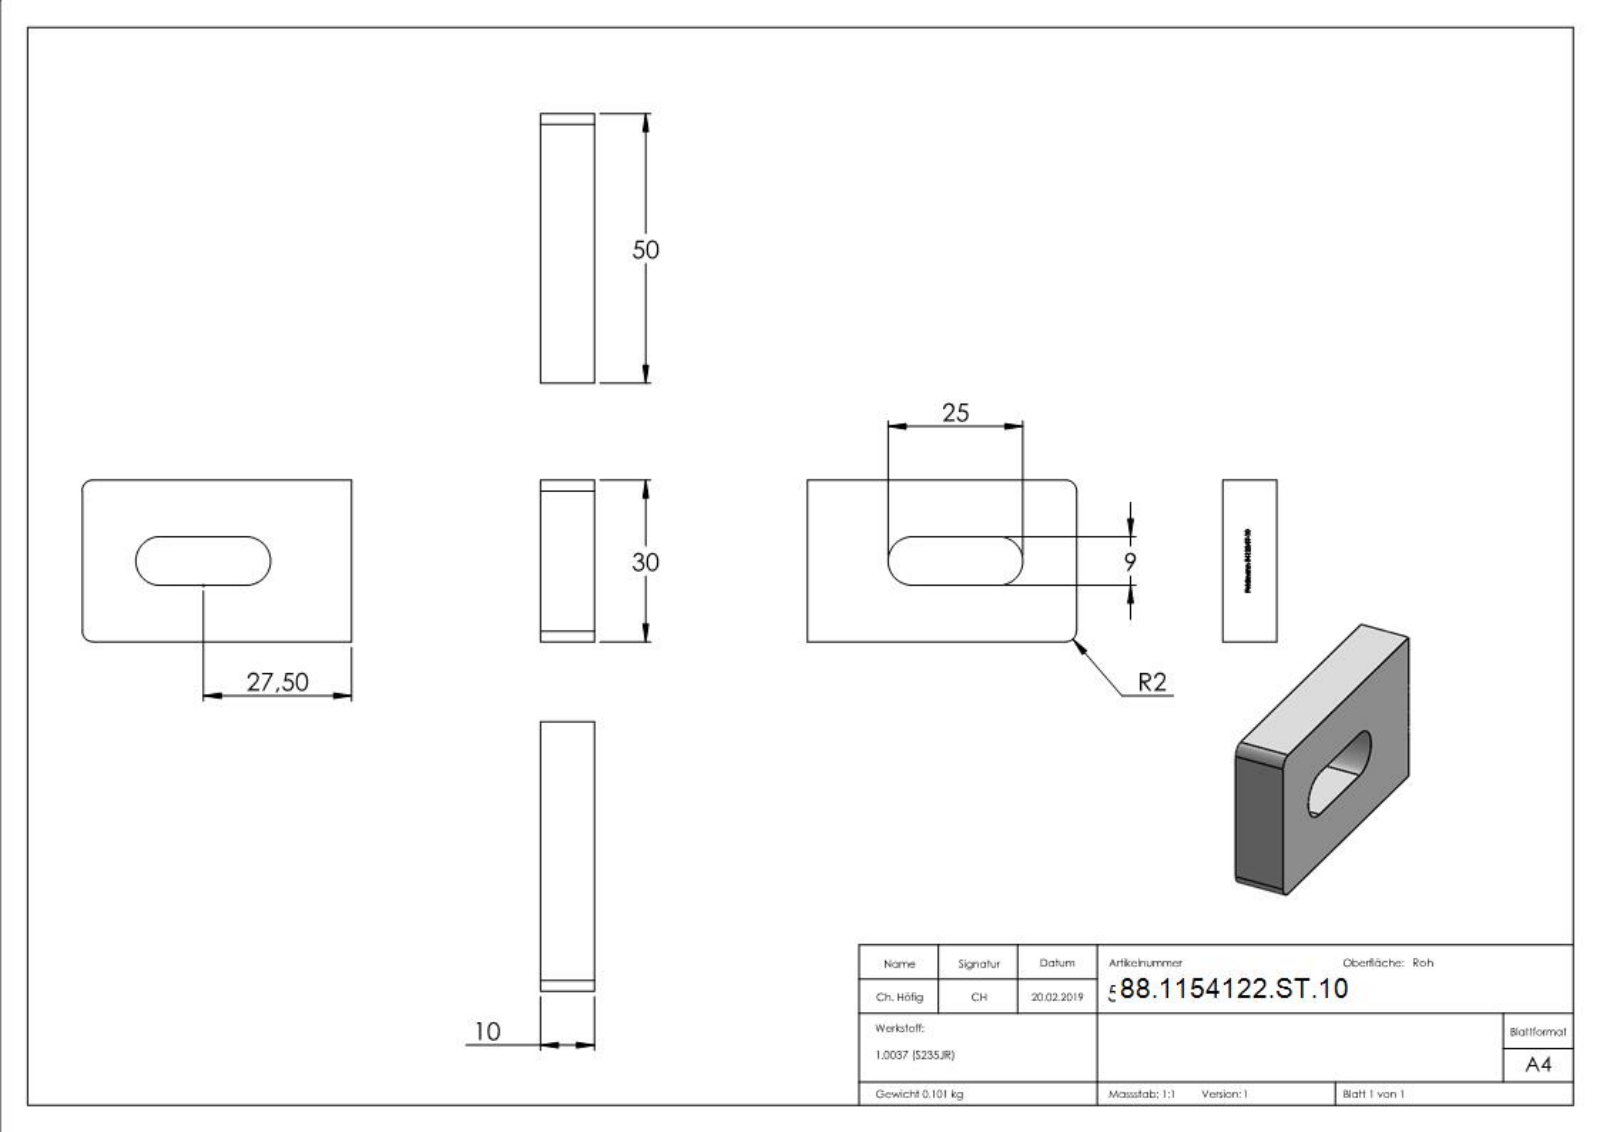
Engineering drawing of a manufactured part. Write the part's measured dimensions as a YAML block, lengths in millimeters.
part_name: "54122-ST-10"
step_written_by: "SolidWorks 2015 (CONFIG_CONTROL_DESIGN)"
units: millimeters
bodies: {solids: 1, faces: 244, planar: 147, cylindrical: 5, other: 92}
overall_size: [50, 30, 10]
volume: 12906
surface_area: 4773
partial_cylinders:
  - {radius: 2, count: 2}
  - {radius: 4.5, count: 2}
face_to_face_distances: [10, 30, 10.5, 19.5, 50, 9, 49.9, 5, 0.45, 0.79]
